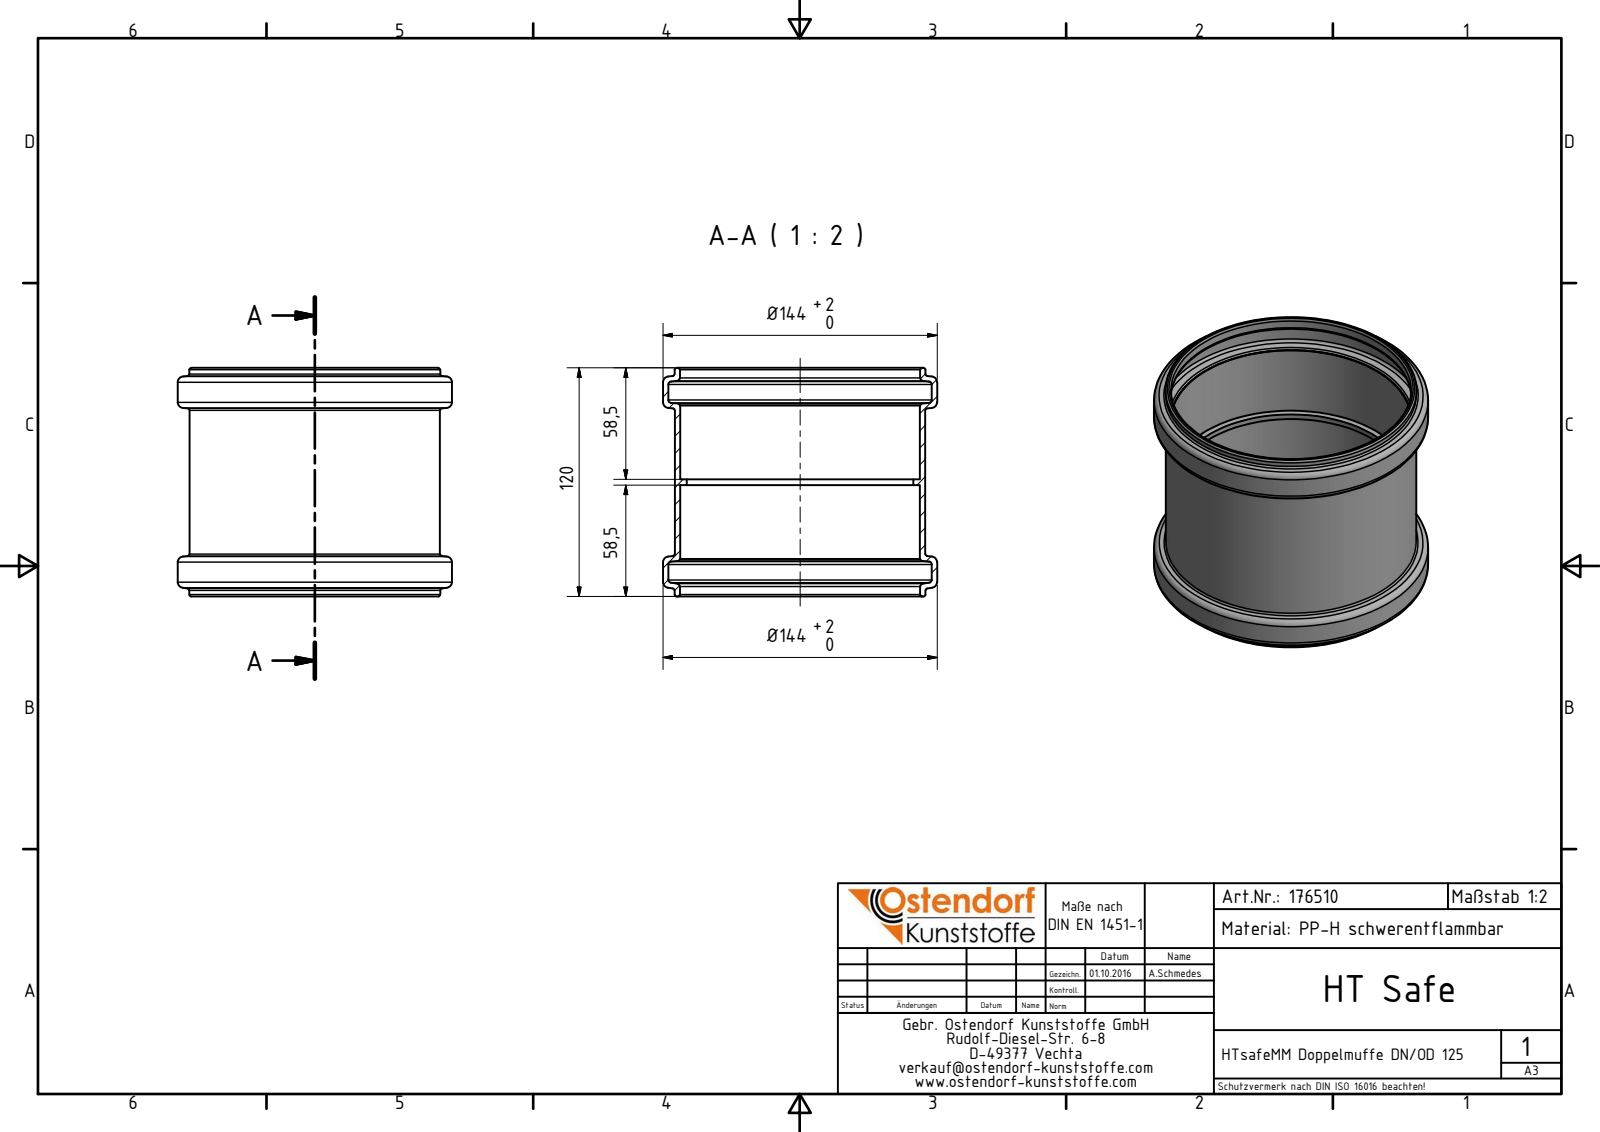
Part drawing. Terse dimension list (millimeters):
name: 176510 HTsafeMM DN_OD 125
written by: Autodesk Inventor 2016 (AUTOMOTIVE_DESIGN)
unit: mm
bodies: 1 solid, 48 faces (6 planar, 14 cylindrical, 28 other)
size: 144 × 144 × 120
volume: 166 706 mm³; area: 118 392 mm²
holes: 1× ⌀119, 1× ⌀125.9, 1× ⌀126.2, 1× ⌀138.4
bosses: 1× ⌀144, 1× ⌀131.8, 1× ⌀131.5
face distances: 3, 58.5, 61.5, 120, 19.77, 100.23, 38.73, 41.73, 80.46
